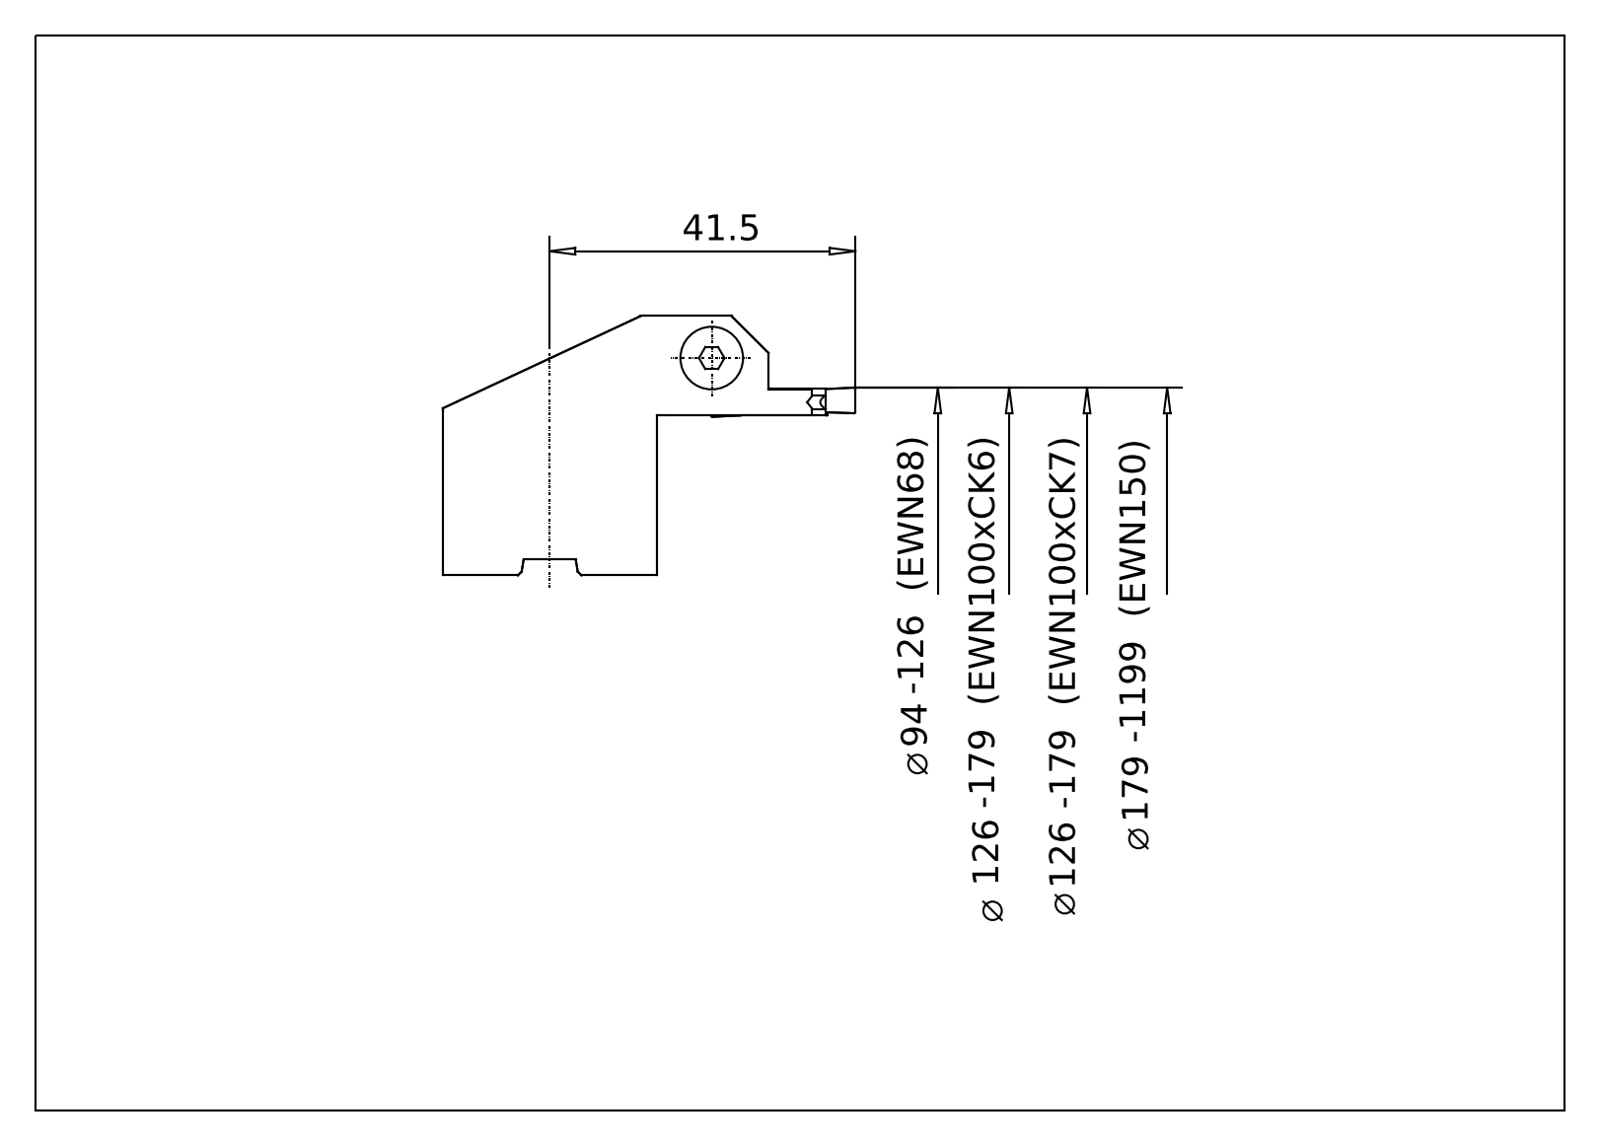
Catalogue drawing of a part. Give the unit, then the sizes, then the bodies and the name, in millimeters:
Units: millimetres
Overall size (bounding box): 57.11 × 35.2 × 29
Round holes (diameter × count): ⌀4.2 ×1, ⌀5.3 ×1, ⌀8.05 ×1, ⌀9 ×1, ⌀14 ×1
Round bosses / shafts (diameter × count): ⌀29 ×1, ⌀8.5 ×1, ⌀5 ×1
Partial cylindrical surfaces — rounded edges, fillets, slot ends (radius × count): R0.2 ×4, R0.1 ×2, R1.25 ×2, R1.63 ×2, R1.26 ×1, R5 ×1
Main face-to-face distances: 21.75, 13.45, 35.2, 33.05, 19.6, 2.15, 15, 1.6, 13.4, 3.5
Hole centre spacings: 12.22
Volume: 19 903 mm³ · Surface area: 7 856 mm²
Bodies: 3 solids, 143 faces (84 planar, 40 cylindrical, 19 other)
Part name (STEP PRODUCT): 626.937 Kaiser ENH 62 S4 94-126|690.183 Kaiser Zyl-Schraube M5x12A_Standard;NONE; 626.937 Kaiser ENH 62 S4 94-126|626.937 Kaiser ENH 62 S4 94-126_Standard;NONE; 626.937 Kaiser ENH 62 S4 94-126|958.425 Kaiser NP 4250 P20C_Einstechplatte 4mm;NONE
STEP written by: ACIS (automotive_design)
